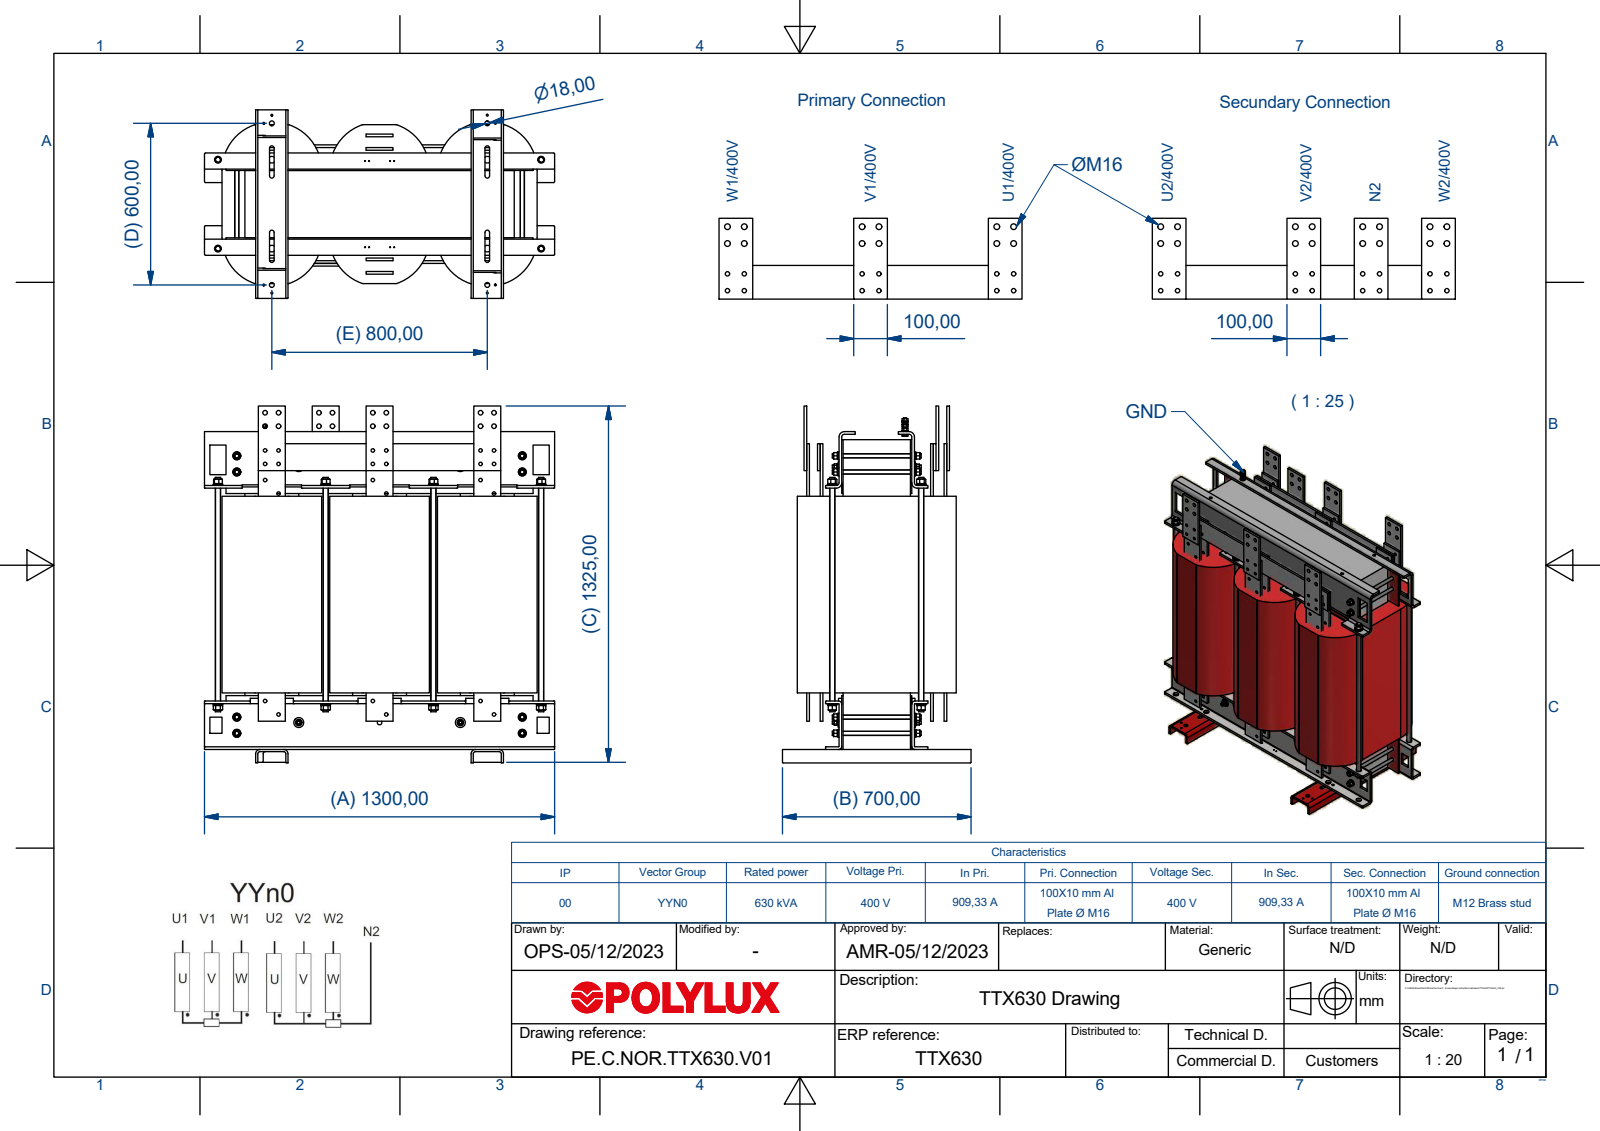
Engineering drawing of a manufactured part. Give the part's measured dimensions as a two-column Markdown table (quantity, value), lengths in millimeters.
| quantity | value |
| --- | --- |
| part name | TTX630_V02 |
| STEP written by | Autodesk Inventor 2018 (AUTOMOTIVE_DESIGN) |
| units | millimeters |
| bodies | 195 solids, 2038 faces (1118 planar, 660 cylindrical, 260 other) |
| overall size | 1325 × 1300 × 700 |
| volume | 570 500 000 mm³ |
| surface area | 20 040 000 mm² |
| round holes (diameter × count) | 13 × 48, 17 × 30, 11 × 24, 25 × 12, 15 × 10, 3.5 × 8, 7 × 8, 13.84 × 8, 17.29 × 8, 21 × 8, 21.2 × 8, 22 × 6 |
| round bosses / shafts (diameter × count) | 37 × 12, 33.6 × 8, 30 × 8, 27.4 × 8, 20 × 8, 16 × 8, 24 × 5, 21.1 × 5 |
| partial cylindrical surfaces (radius × count) | 4 × 32, 12.5 × 12, 179.21 × 12, 8.5 × 8, 8 × 6, 2 × 4, 10 × 4, 12 × 4 |
| main face-to-face distances | 400, 10, 85, 200, 250, 50, 5, 255, 70, 340 |
| hole center spacings | 400, 300, 330, 100, 600, 200, 800, 518.56 |
